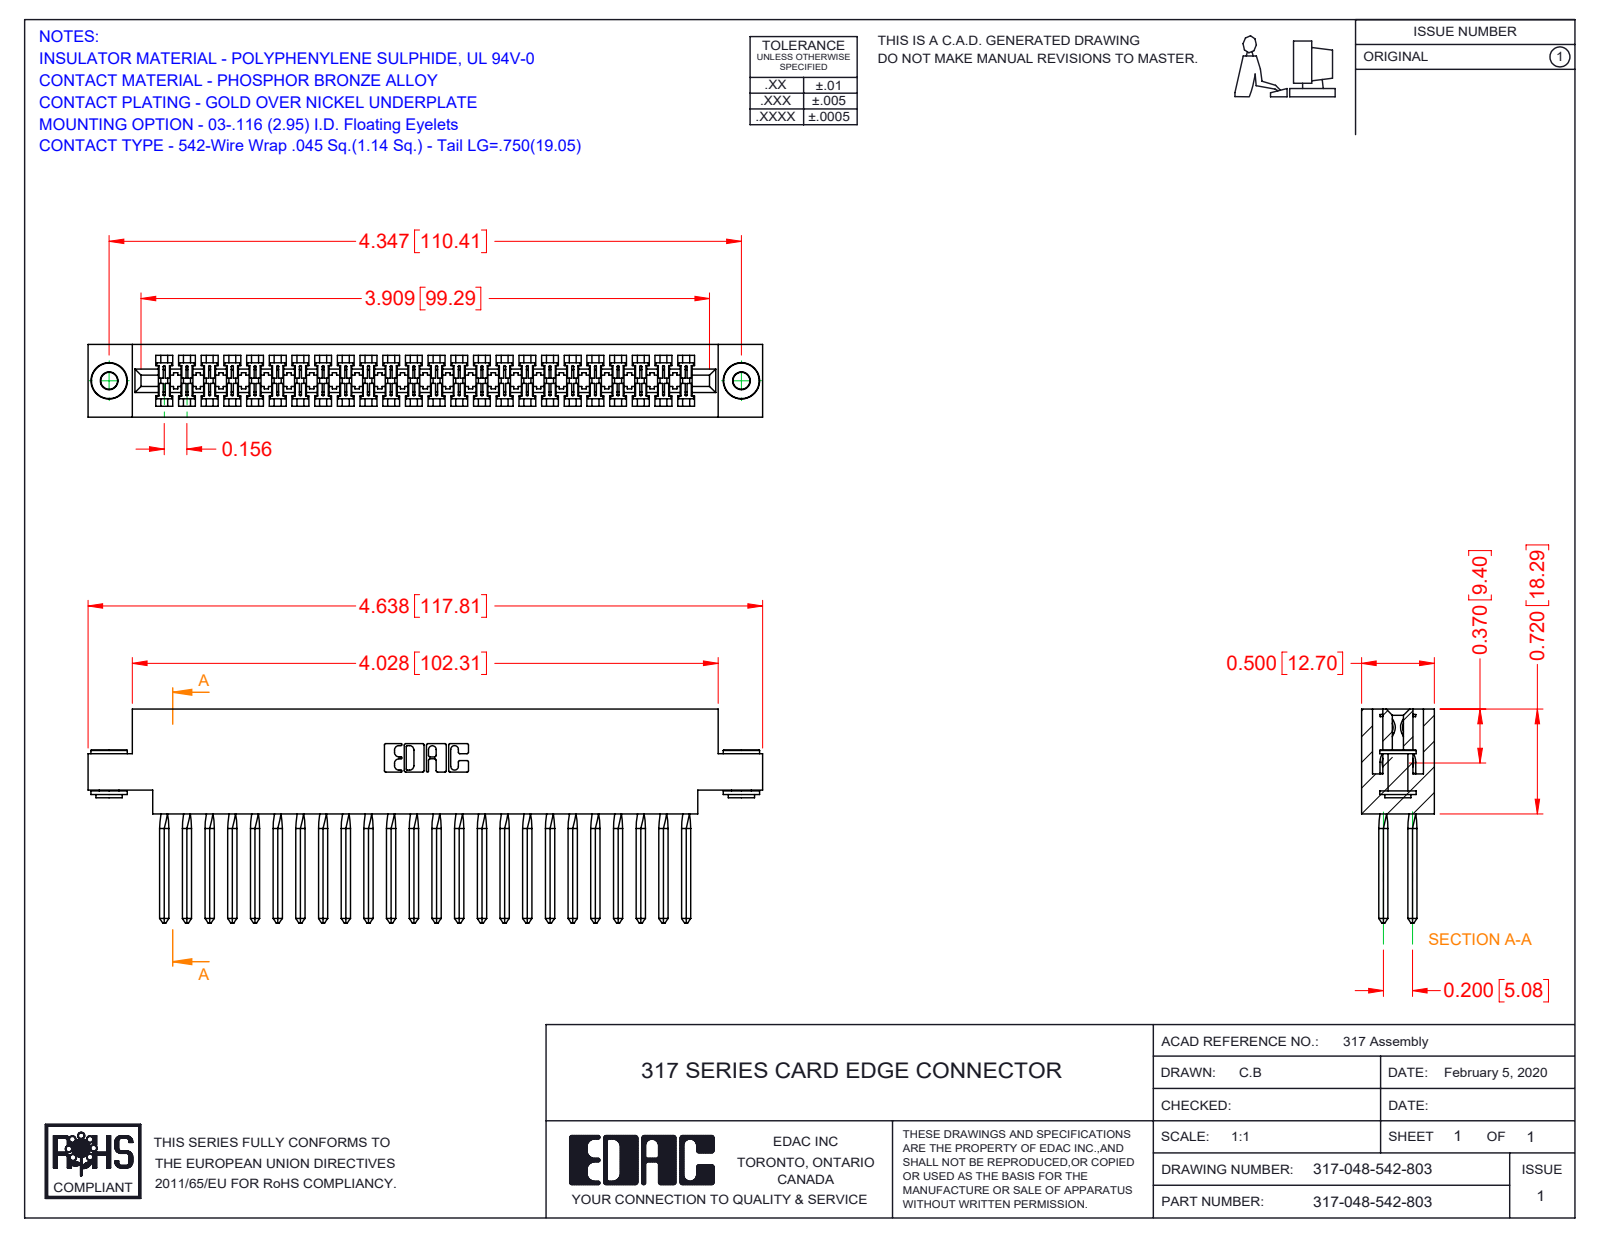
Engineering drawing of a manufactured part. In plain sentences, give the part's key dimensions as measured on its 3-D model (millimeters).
The part is named "317-048-542-803; 317 Part_.156 Dia - TH; 345-250-002_345-250-002-102; 317-290-003_542". Its 3-D file was written by "SolidWorks 2016 (CONFIG_CONTROL_DESIGN)". It is 51 solids with 2876 faces: 2276 planar, 400 cylindrical and 200 other. Overall it measures 117.8 by 37.3 by 12.7 millimeters. Its volume is 18 750 cubic millimeters and its surface area 25 700 square millimeters. Round holes: 2 of diameter 2.9, 2 of diameter 4. Round bosses or shafts: 2 of diameter 6.4, 2 of diameter 4.6, 2 of diameter 3.5. Partial cylindrical surfaces (rounded edges, fillets, slot ends): 96 of radius 0.2, 22 of radius 0.3, 6 of radius 0.2, 6 of radius 0.8, 3 of radius 0.7, 2 of radius 1.9, 2 of radius 2.3, 2 of radius 2.5. The main face-to-face distances are 12.7, 1.9, 10.8, 8.9, 2.8, 5.1, 2.9, 1.2, 3.5, 18.3. The hole center spacings are 110.4.
